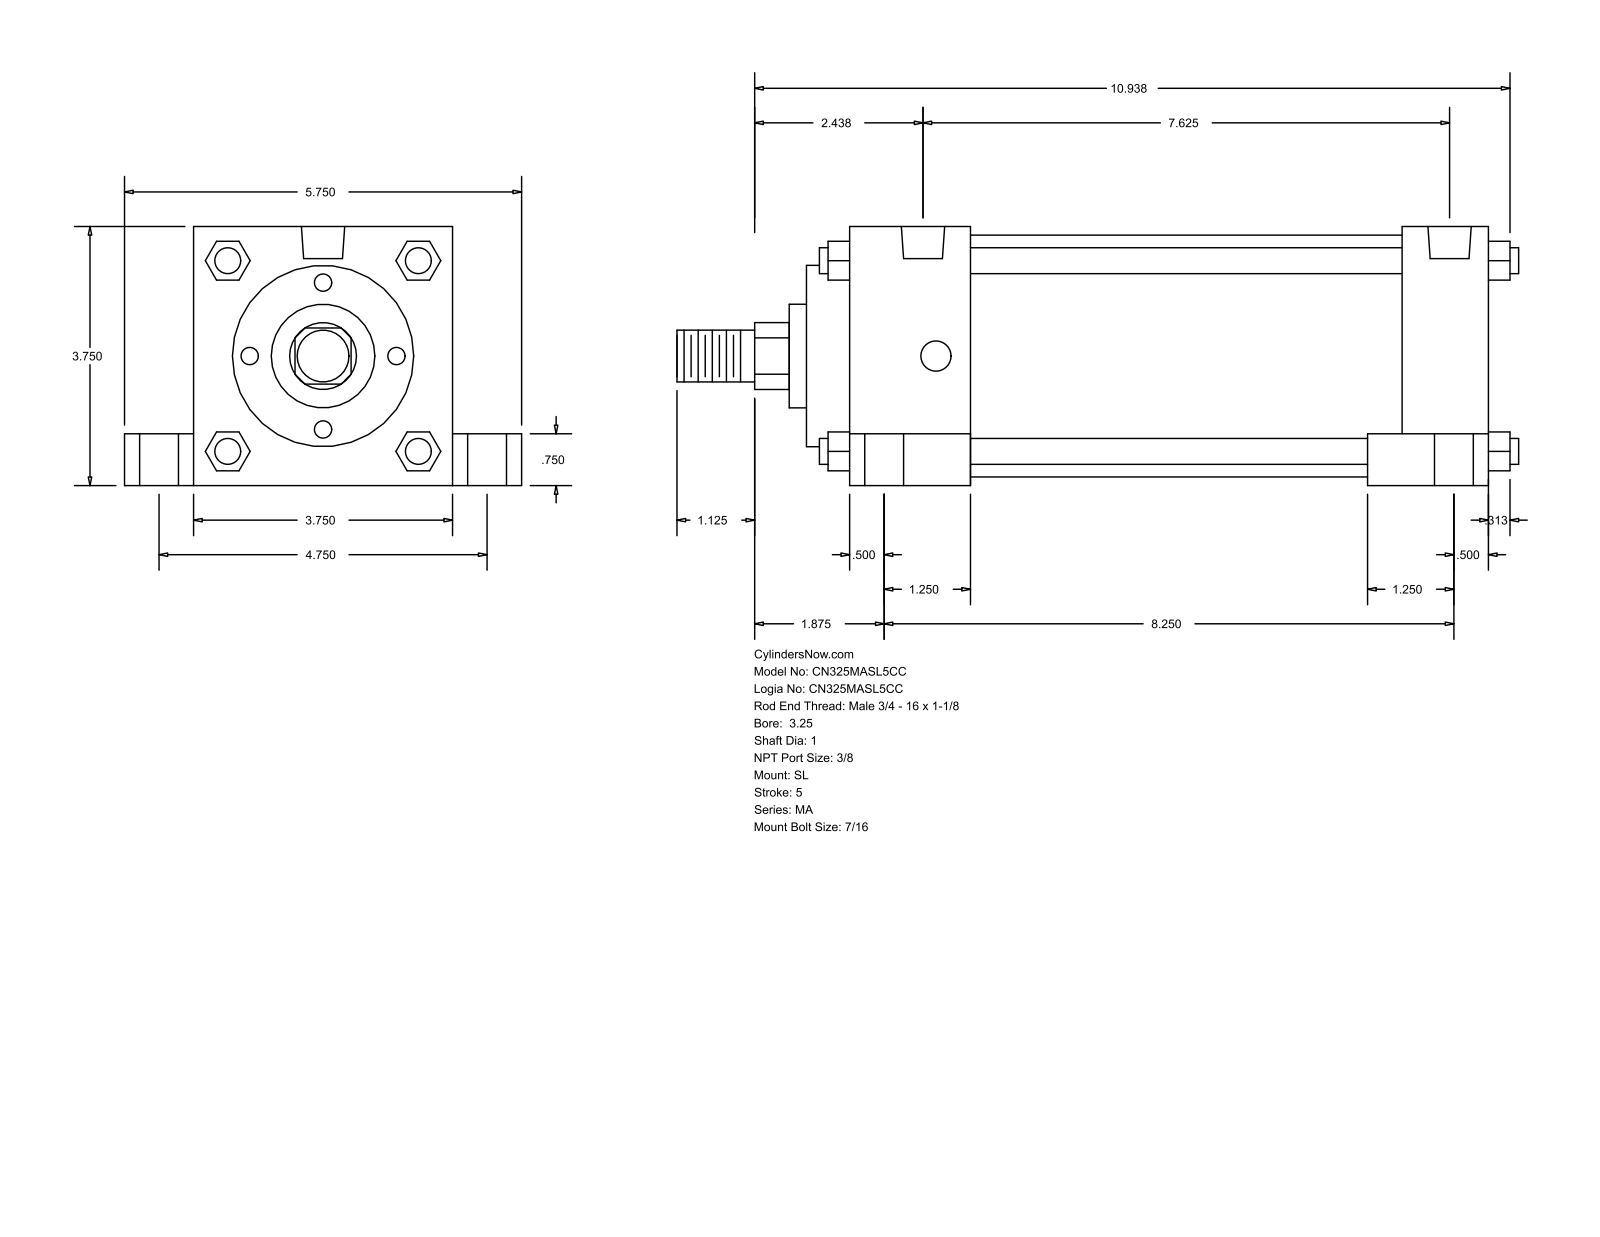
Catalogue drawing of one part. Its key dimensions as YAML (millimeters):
part_name: "MA_SL__0325_1"
step_written_by: "GSSL Pune (CONFIG_CONTROL_DESIGN)"
units: millimeters
bodies: {solids: 0, faces: 150, planar: 113, cylindrical: 37, other: 0}
overall_size: [309.56, 146.05, 95.25]
round_holes:
  - {diameter: 11.11, count: 4}
  - {diameter: 14.29, count: 4}
  - {diameter: 20.64, count: 4}
  - {diameter: 15.93, count: 2}
round_bosses_or_shafts:
  - {diameter: 9.53, count: 4}
  - {diameter: 88.9, count: 1}
  - {diameter: 66.67, count: 1}
  - {diameter: 38.1, count: 1}
  - {diameter: 25.4, count: 1}
  - {diameter: 19.05, count: 1}
partial_cylinders:
  - {radius: 12.29, count: 1}
face_to_face_distances: [95.24, 234.96, 15.87, 25.41, 120.65, 19.05, 203.2, 31.76, 44.46, 158.74]
hole_center_spacings: [60.35, 60.66, 62, 63.27, 120.66, 184.15, 199.83, 204.38]
